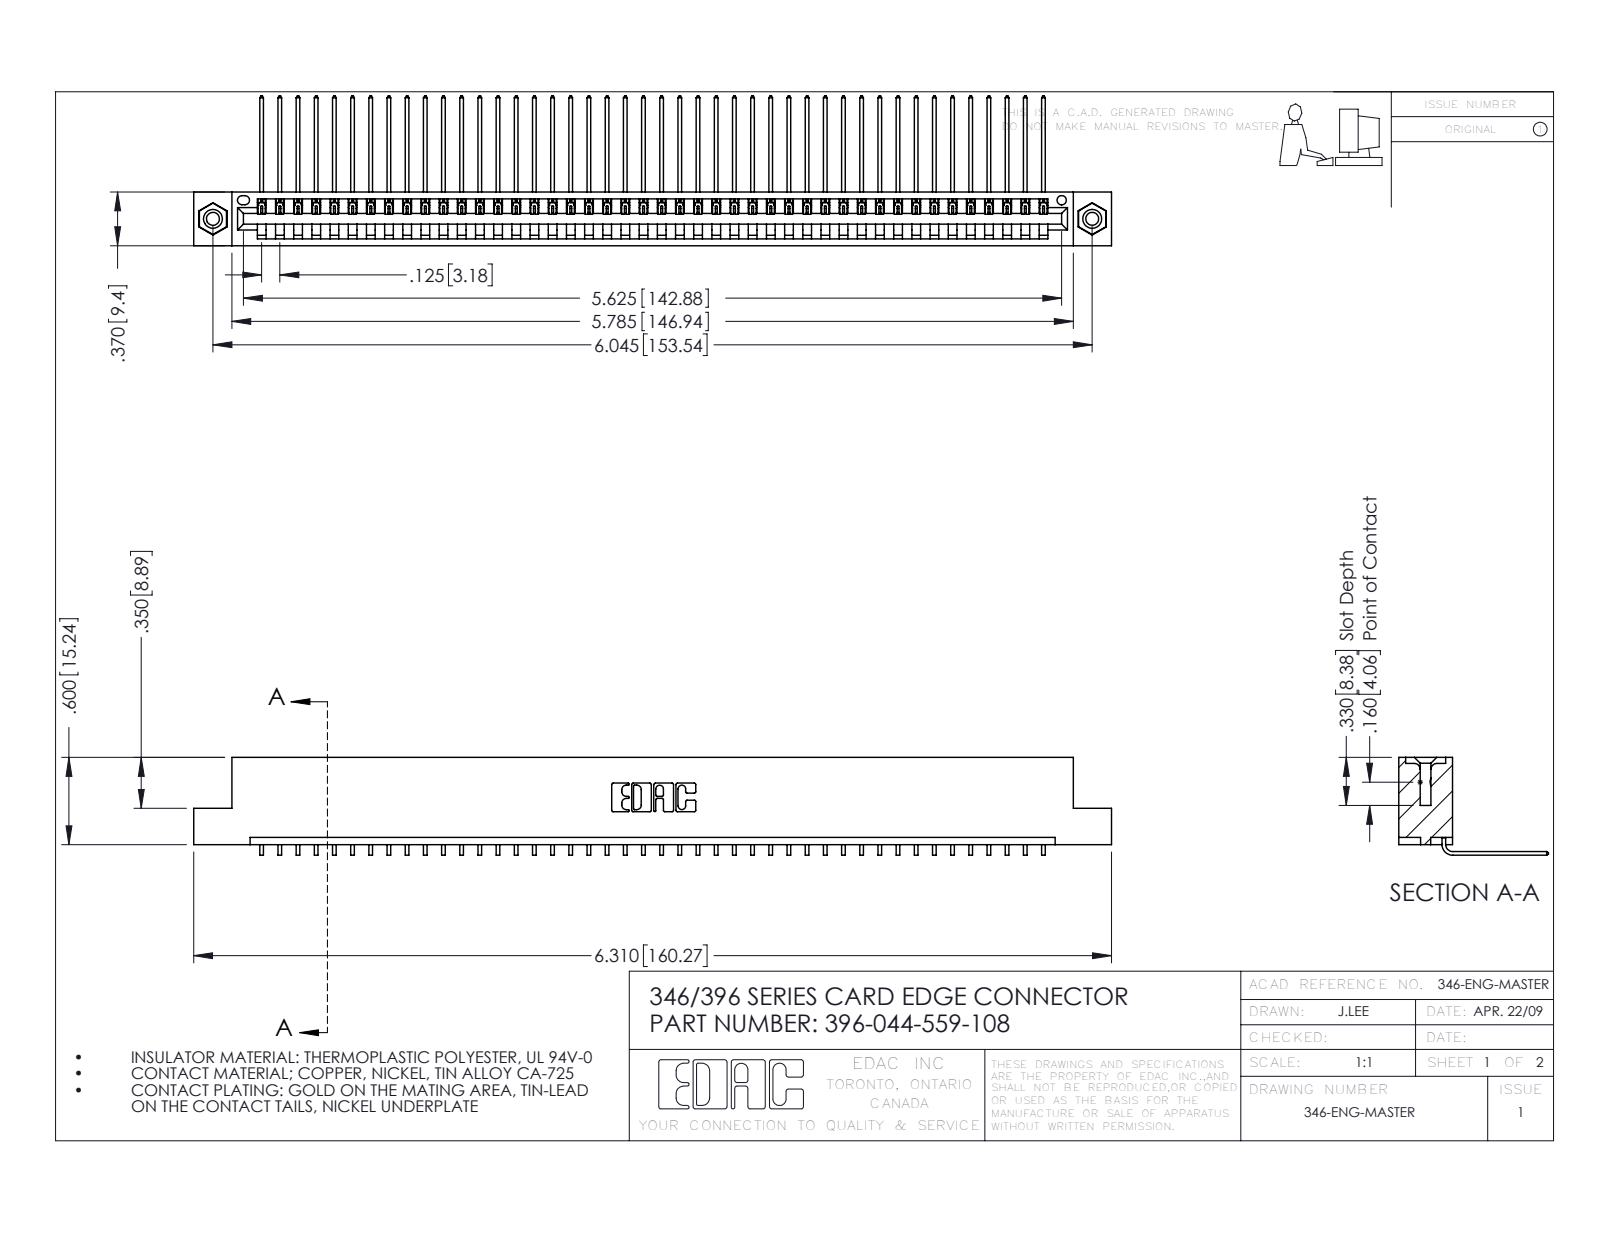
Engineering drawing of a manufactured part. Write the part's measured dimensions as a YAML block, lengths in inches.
part_name: "346 Part_Flush Mounting Lugs - 0.156 Dia-TI; 345-292-001_558 559 Tail - 1; 345-250-001_345-250-003-102; 396-044-559-108"
step_written_by: "SolidWorks 2016 (CONFIG_CONTROL_DESIGN)"
units: inches
bodies: {solids: 47, faces: 2822, planar: 1956, cylindrical: 850, other: 16}
overall_size: [6.31, 1.03, 0.673]
volume: 0.946
surface_area: 31.44
round_holes:
  - {diameter: 0.089, count: 2}
  - {diameter: 0.125, count: 2}
  - {diameter: 0.156, count: 2}
  - {diameter: 0.064, count: 1}
round_bosses_or_shafts:
  - {diameter: 0.155, count: 2}
partial_cylinders:
  - {radius: 0.006, count: 88}
  - {radius: 0.01, count: 22}
  - {radius: 0.007, count: 6}
  - {radius: 0.031, count: 6}
  - {radius: 0.026, count: 3}
  - {radius: 0.031, count: 2}
  - {radius: 0.04, count: 2}
  - {radius: 0.014, count: 1}
face_to_face_distances: [0.048, 0.322, 0.37, 0.025, 0.25, 0.072, 0.298, 0.148, 0.222, 0.1]
hole_center_spacings: [0.246, 5.836, 6.045]
